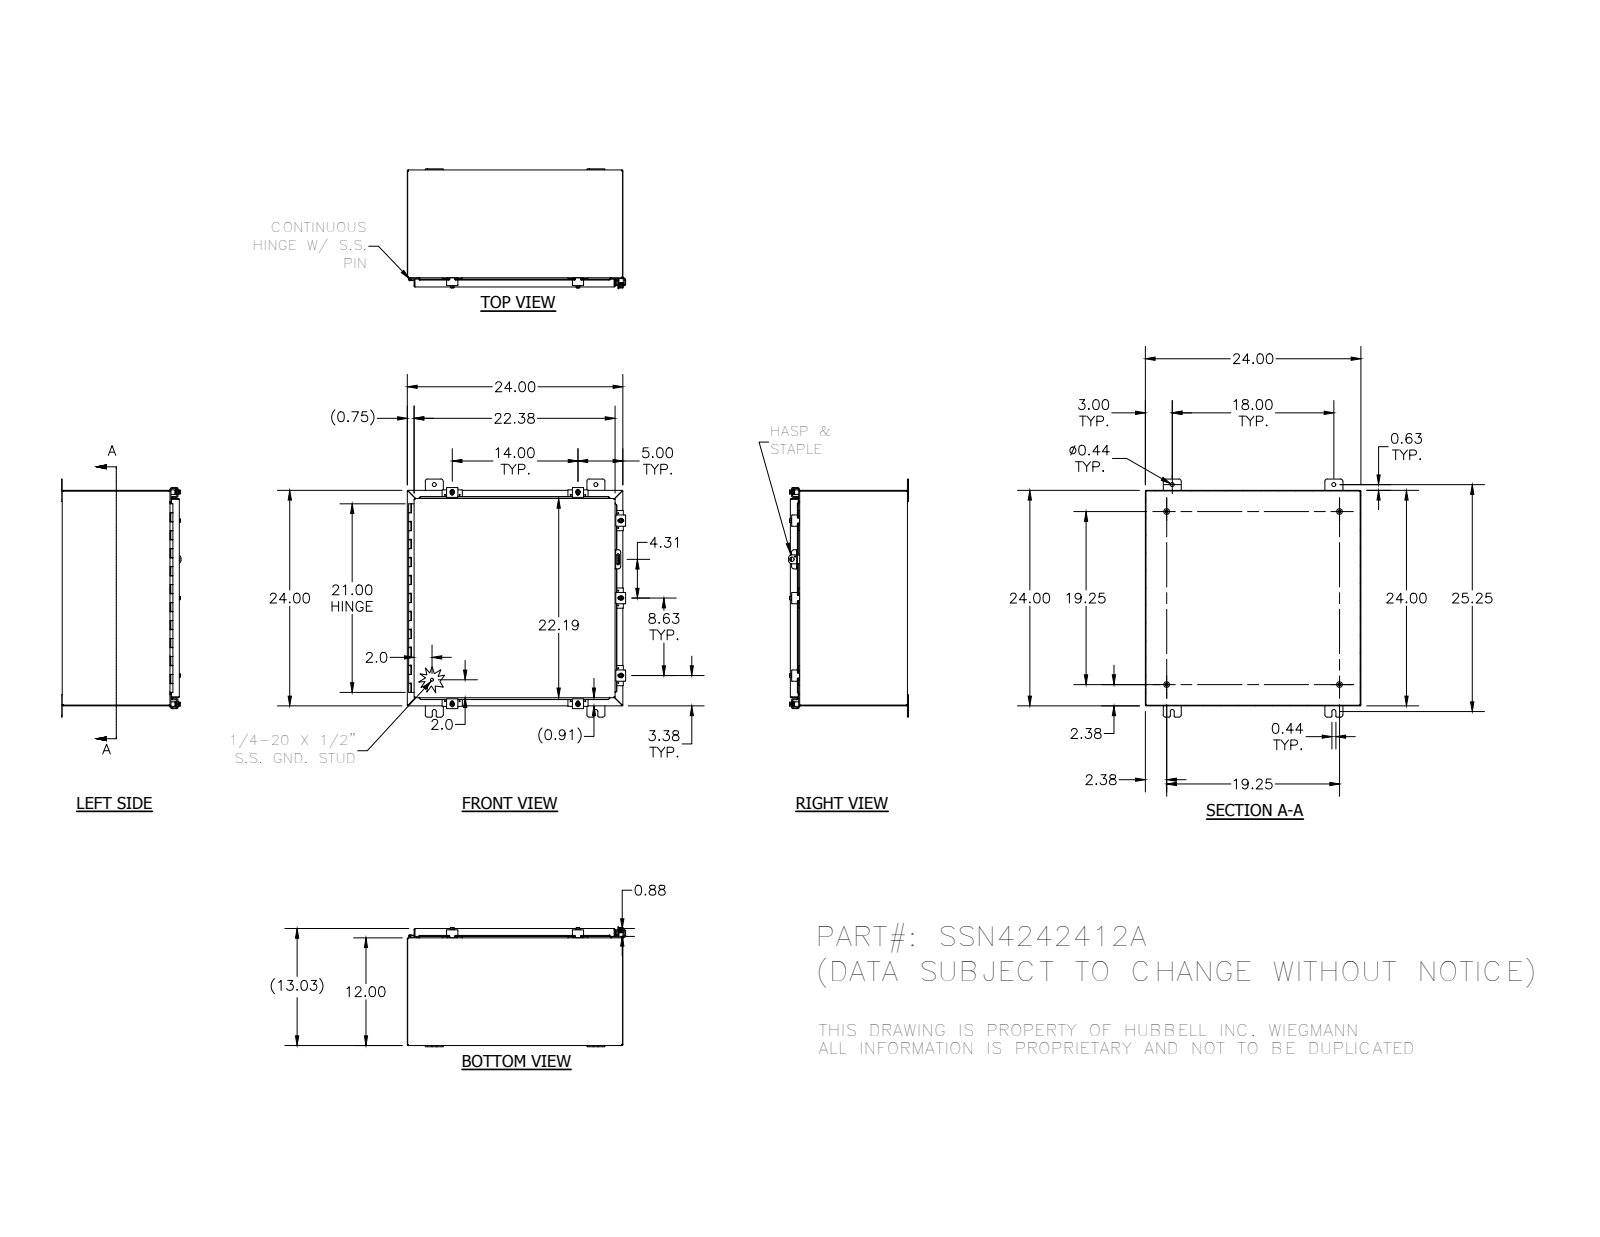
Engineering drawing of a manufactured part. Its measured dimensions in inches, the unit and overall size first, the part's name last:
Units: inches
Overall size (bounding box): 26.5 × 24.216 × 13.355
Round holes (diameter × count): ⌀0.11 ×14, ⌀0.211 ×7, ⌀0.281 ×7, ⌀0.3 ×7, ⌀0.438 ×4, ⌀0.125 ×1, ⌀0.156 ×1, ⌀0.5 ×1
Round bosses / shafts (diameter × count): ⌀0.25 ×9, ⌀0.52 ×7, ⌀0.5 ×7, ⌀0.35 ×7, ⌀0.625 ×4, ⌀0.33 ×4, ⌀0.337 ×1, ⌀0.12 ×1
Partial cylindrical surfaces — rounded edges, fillets, slot ends (radius × count): R0.03 ×83, R0.125 ×37, R0.25 ×33, R0.031 ×23, R0.105 ×23, R0.062 ×18, R0.141 ×14, R0.1 ×10
Main face-to-face distances: 0.074, 23.926, 12.959, 24, 23.852, 12.885, 13.033, 11.926, 1.033, 12
Hole centre spacings: 0.876, 23.303, 14, 1.625, 13.191, 14.816, 19.639, 22.961
Volume: 203.5 in³ · Surface area: 5 363 in²
Bodies: 52 solids, 2024 faces (782 planar, 875 cylindrical, 367 other)
Part name (STEP PRODUCT): 32874-24; 32874-24P; 32874-24L; 32874-24T (+8 more)
STEP written by: SolidWorks 2014 (AUTOMOTIVE_DESIGN)
